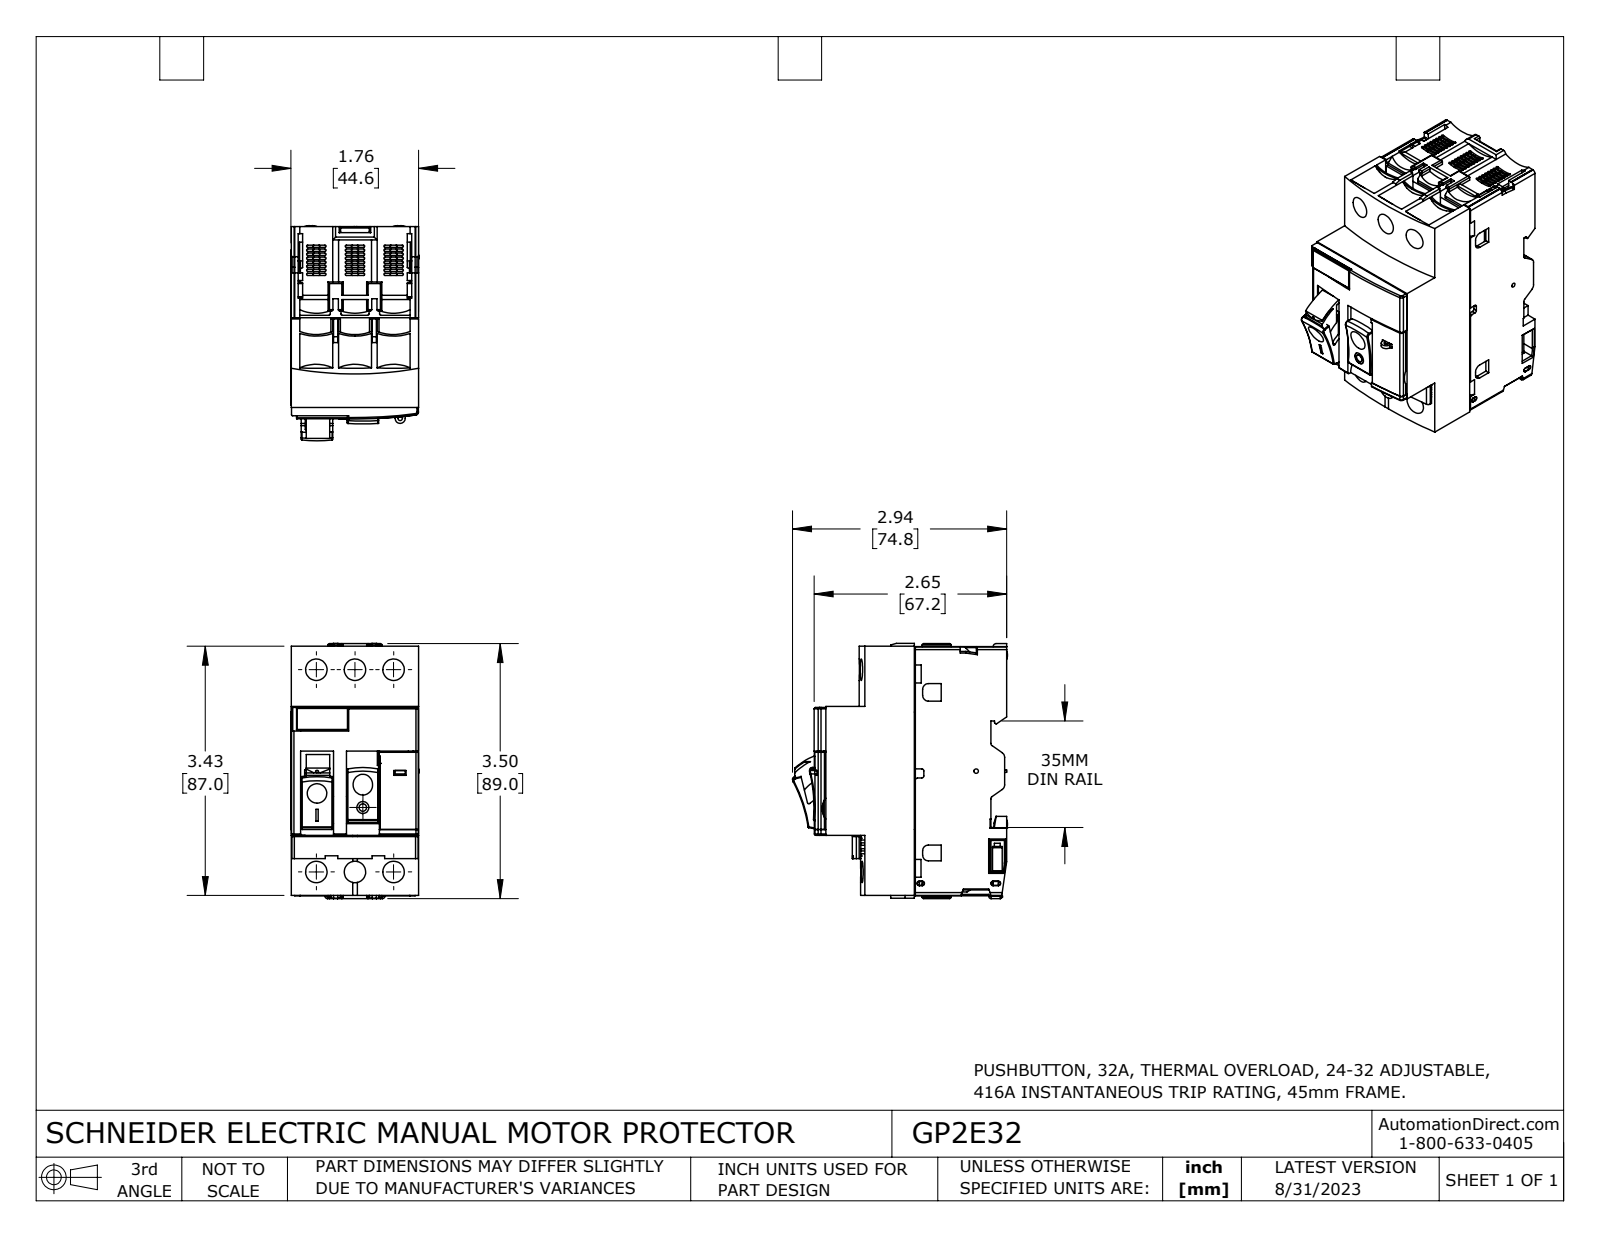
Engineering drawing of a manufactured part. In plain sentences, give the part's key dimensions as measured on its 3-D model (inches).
The part is named "GP2E32". Its 3-D file was written by "SolidWorks 2021 (CONFIG_CONTROL_DESIGN)". It is 15 solids with 2269 faces: 1521 planar, 657 cylindrical and 91 other. Overall it measures 3.508 by 2.957 by 1.764 inches. Its volume is 11.58 cubic inches and its surface area 98.93 square inches. Round holes: 6 of diameter 0.295, 5 of diameter 0.197, 2 of diameter 0.059, 1 of diameter 0.157, 1 of diameter 0.165, 1 of diameter 0.315, 1 of diameter 0.327, 1 of diameter 0.335, 1 of diameter 0.343. Round bosses or shafts: 2 of diameter 0.244, 2 of diameter 0.118, 1 of diameter 0.382, 1 of diameter 0.102, 1 of diameter 0.047. Partial cylindrical surfaces (rounded edges, fillets, slot ends): 104 of radius 0.016, 47 of radius 0.02, 16 of radius 0.039, 12 of radius 0.01, 12 of radius 0.012, 12 of radius 0.031, 8 of radius 0.059, 6 of radius 0.004. The main face-to-face distances are 1.752, 0.531, 0.115, 1.233, 1.756, 0.059, 1.637, 0.581, 1.053, 1.171. The hole center spacings are 0.531, 2.83, 2.779, 0.346, 0.402, 0.546, 0.671, 0.726.
